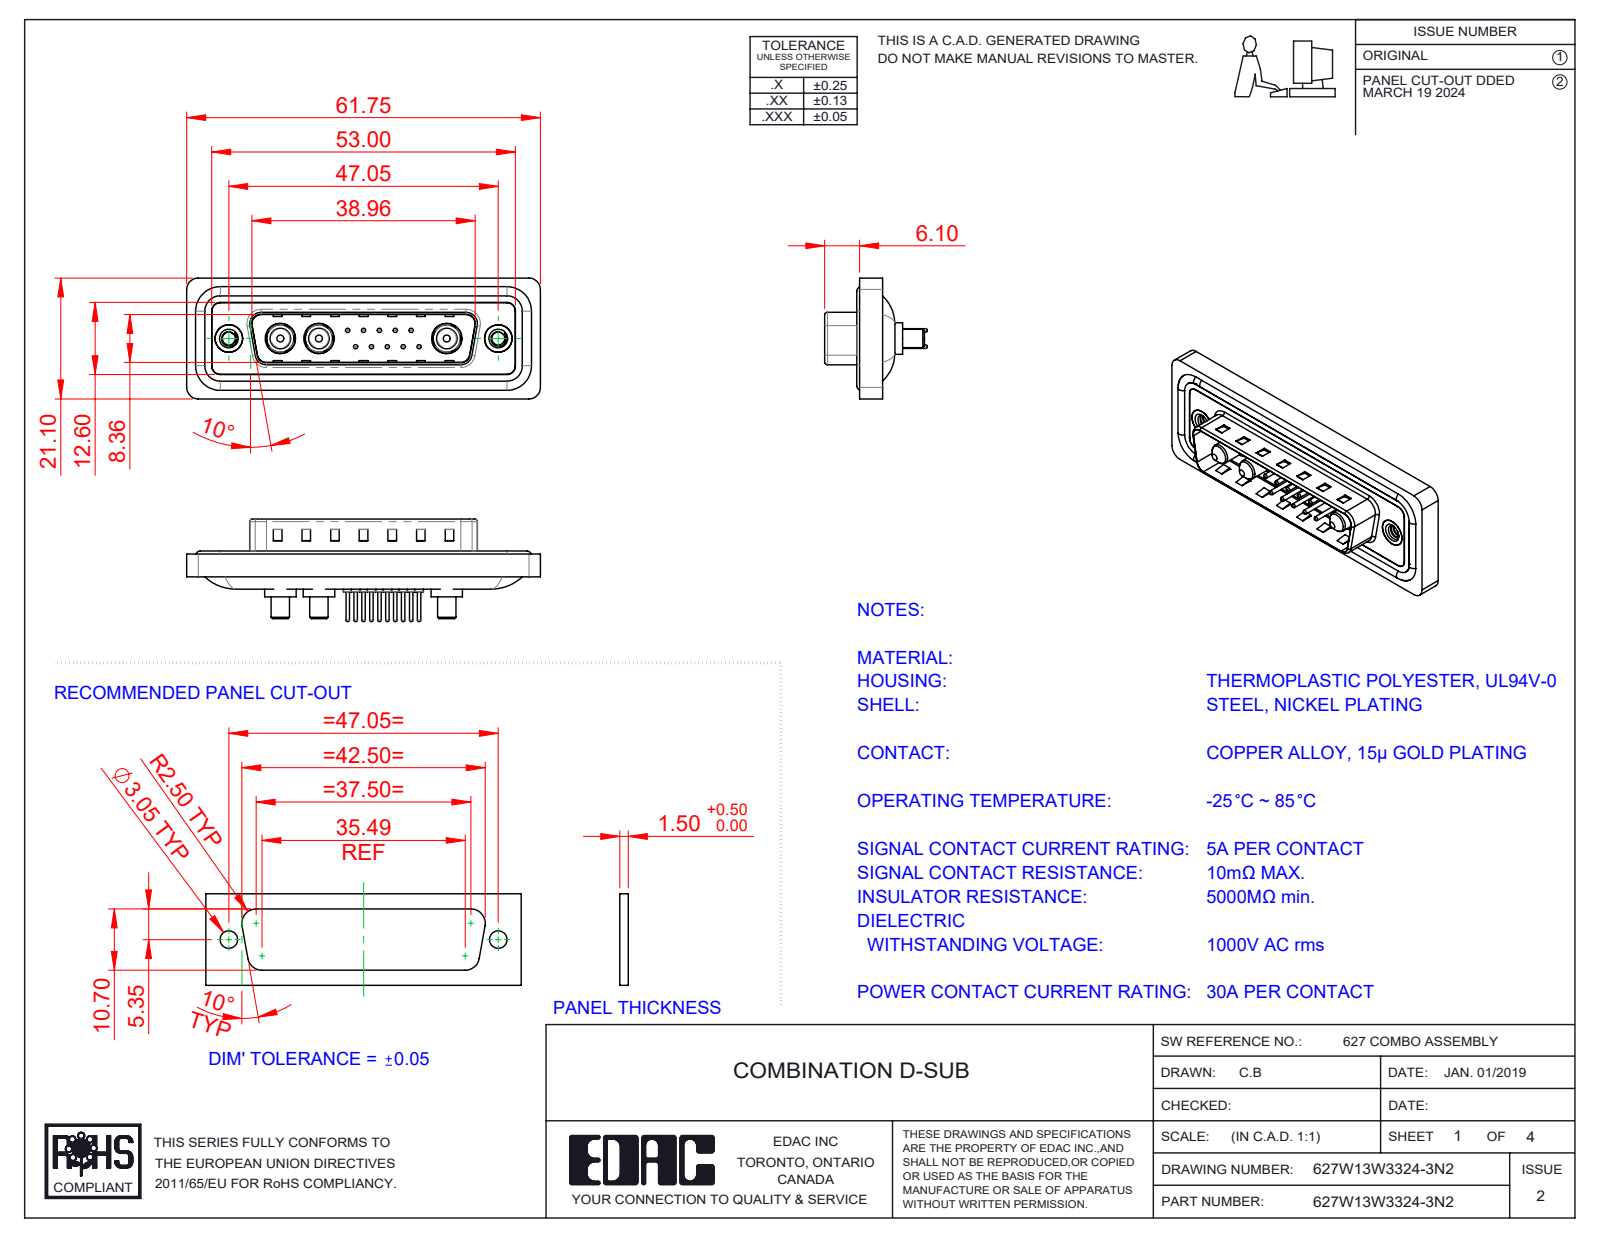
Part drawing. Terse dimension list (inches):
name: 627Combo Threaded Rivet_2; 627Combo Waterproof Housing_25 Contacts; 627Combo Shell Rear_25 Contacts; 627W13W3324-3N2 (+5 more)
written by: SolidWorks 2023 (CONFIG_CONTROL_DESIGN)
unit: in
bodies: 23 solids, 970 faces (309 planar, 385 cylindrical, 276 other)
size: 2.431 × 0.831 × 0.705
volume: 0.449 in³; area: 18.43 in²
holes: 10× ⌀0.03, 10× ⌀0.063, 10× ⌀0.079, 3× ⌀0.191, 3× ⌀0.209, 2× ⌀0.089, 2× ⌀0.157, 2× ⌀0.189, 2× ⌀0.197
bosses: 10× ⌀0.059, 10× ⌀0.024, 4× ⌀0.063, 3× ⌀0.217, 3× ⌀0.205, 3× ⌀0.187, 3× ⌀0.148, 3× ⌀0.142
rounds: 22× R0.059, 18× R0.079, 8× R0.02, 8× R0.063, 4× R0.01, 4× R0.024, 4× R0.026, 4× R0.035
face distances: 0.016, 0.059, 0.043, 0.063, 0.02, 0.122, 0.114, 0.032, 0.377, 0.161
hole spacings: 0.124, 0.109, 0.198, 0.218, 0.295, 0.198, 0.327, 0.398
